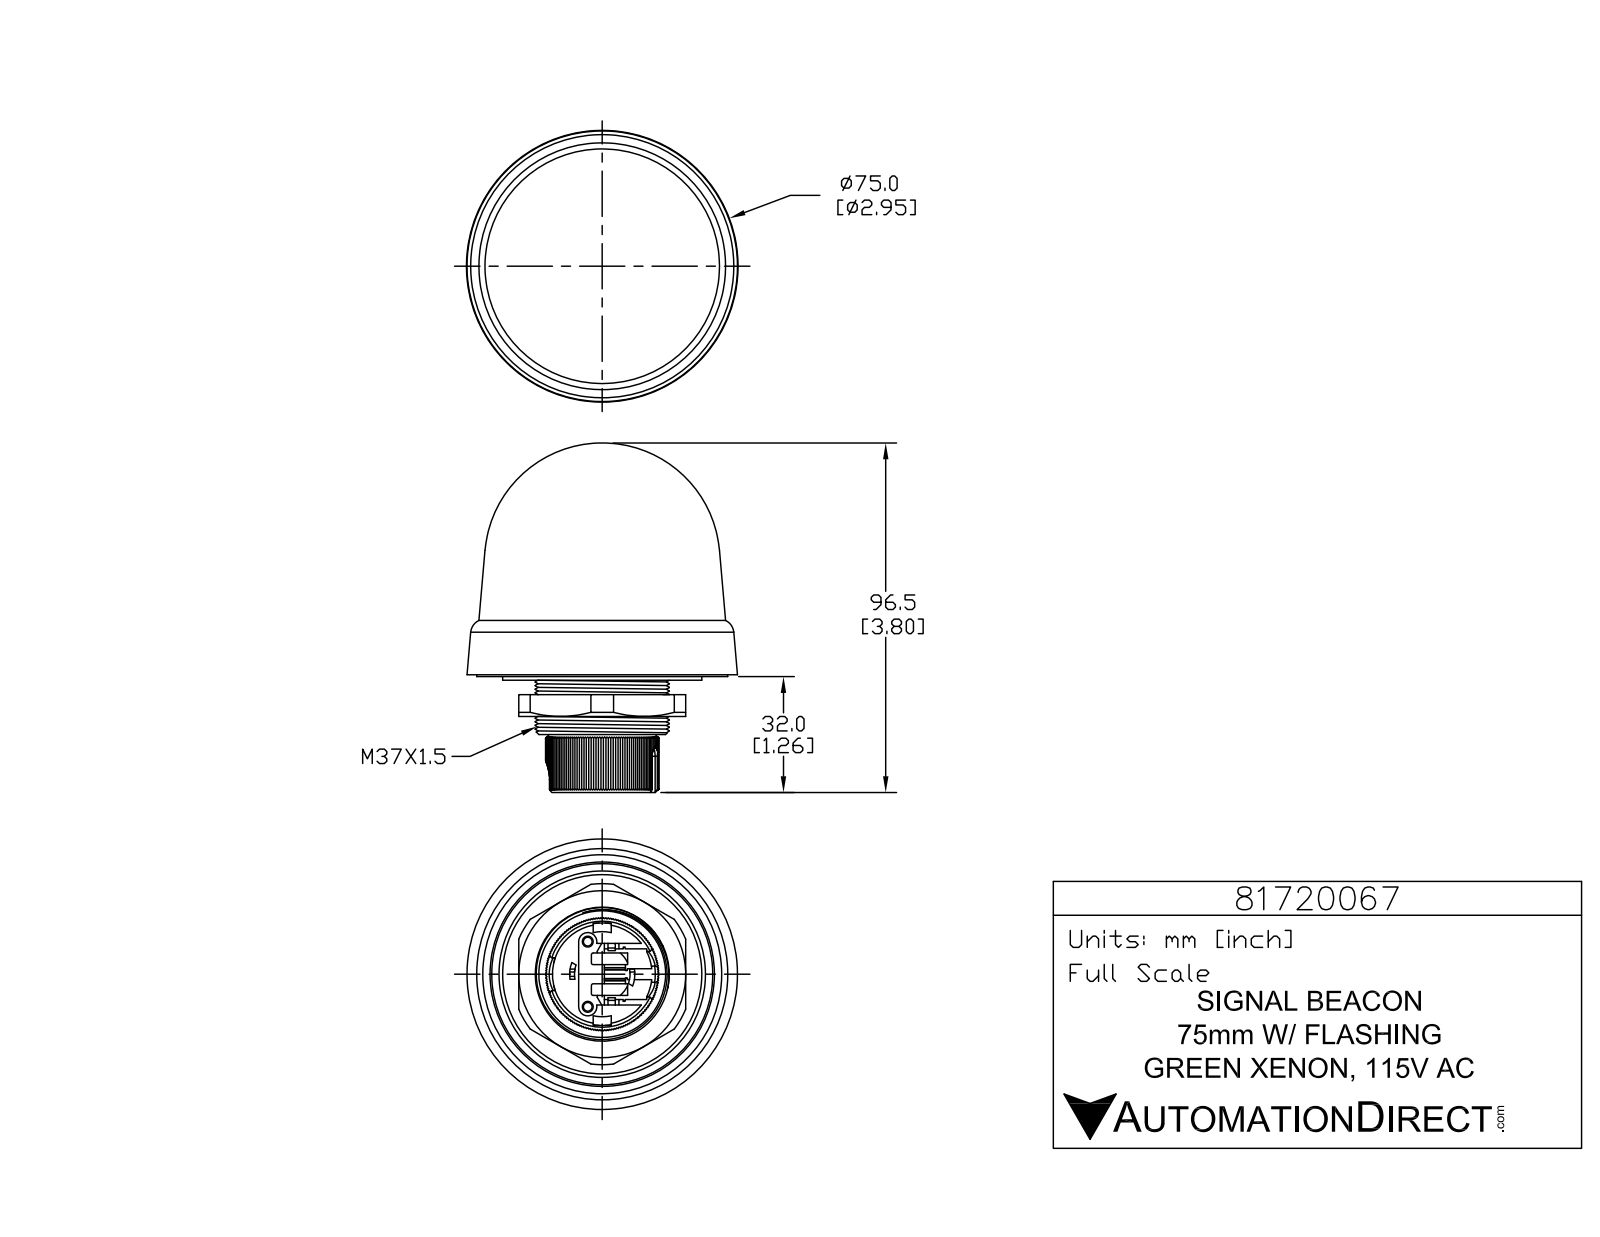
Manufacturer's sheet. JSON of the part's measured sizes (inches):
{"part_name": "81720067", "step_written_by": "SolidWorks 2019 (CONFIG_CONTROL_DESIGN)", "units": "inches", "bodies": {"solids": 3, "faces": 560, "planar": 432, "cylindrical": 80, "other": 48}, "overall_size": [3.799, 2.941, 2.941], "volume_in3": 12.36, "surface_area_in2": 58.68, "round_holes": [[0.094, 2], [0.118, 2], [0.604, 1], [1.142, 1]], "round_bosses_or_shafts": [[0.217, 2], [0.067, 2], [2.165, 1], [1.457, 1], [0.925, 1]], "partial_cylinders_radius": [[0.008, 6], [0.039, 6], [0.02, 4], [0.031, 2], [0.079, 2], [0.098, 2], [0.177, 1], [0.354, 1]], "face_to_face_distances": [0.177, 0.354, 0.197, 0.433, 0.512, 0.335, 0.059, 0.394, 0.118, 0.157], "hole_center_spacings": [0.388, 0.709]}
